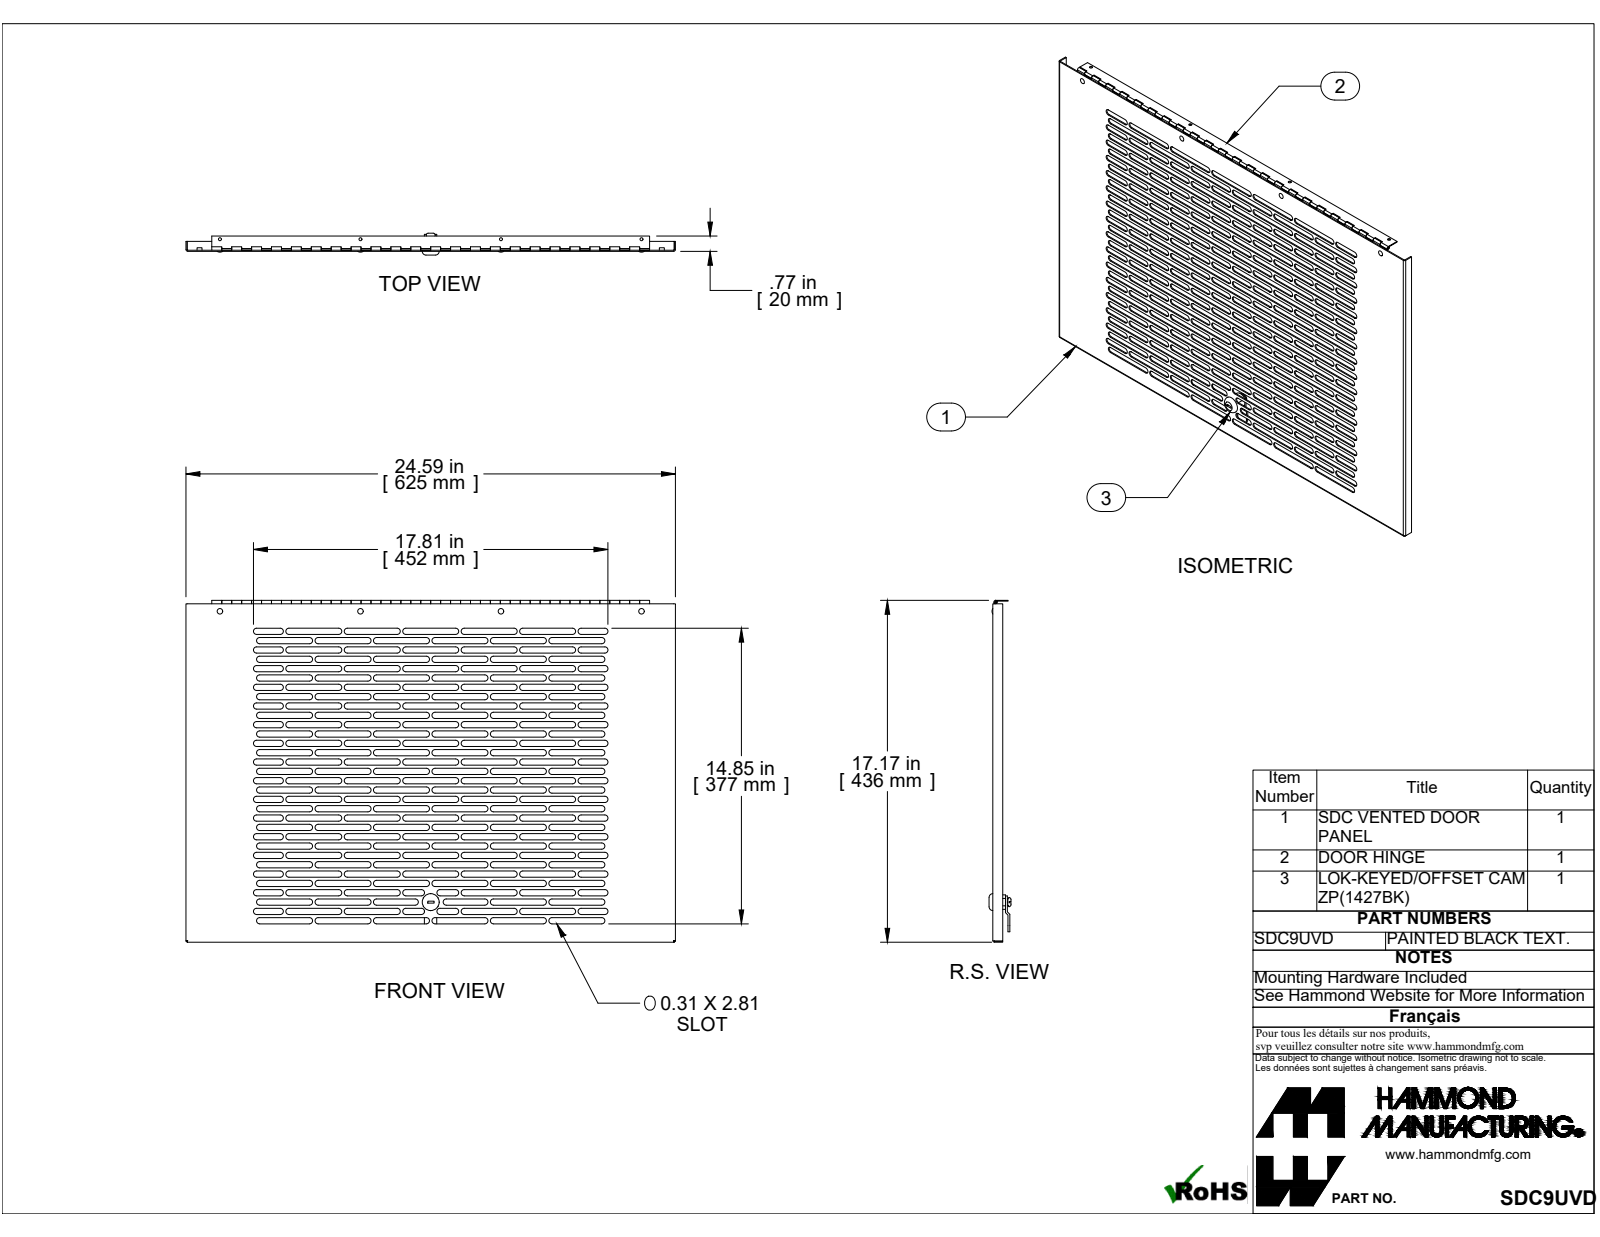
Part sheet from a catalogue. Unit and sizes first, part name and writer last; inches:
Units: inches
Overall size (bounding box): 24.594 × 17.174 × 1.1
Round holes (diameter × count): ⌀0.15 ×8, ⌀0.126 ×4, ⌀0.092 ×1, ⌀0.204 ×1, ⌀0.597 ×1
Round bosses / shafts (diameter × count): ⌀0.728 ×1, ⌀0.232 ×1, ⌀0.174 ×1, ⌀0.08 ×1
Partial cylindrical surfaces — rounded edges, fillets, slot ends (radius × count): R0.156 ×344, R0.156 ×64, R0.156 ×12, R0.029 ×3, R0.086 ×3, R0.31 ×2, R0.38 ×1
Main face-to-face distances: 0.057, 0.041, 0.057, 24.537, 0.098, 17.076, 17.117, 17.133, 17.174, 1.876
Hole centre spacings: 7.063, 14.125, 7.062, 15.028, 18.044, 21.187
Volume: 18 in³ · Surface area: 714.4 in²
Bodies: 14 solids, 1253 faces (698 planar, 539 cylindrical, 16 other)
Part name (STEP PRODUCT): SDC9UVD
STEP written by: SolidWorks 2019 (CONFIG_CONTROL_DESIGN)
